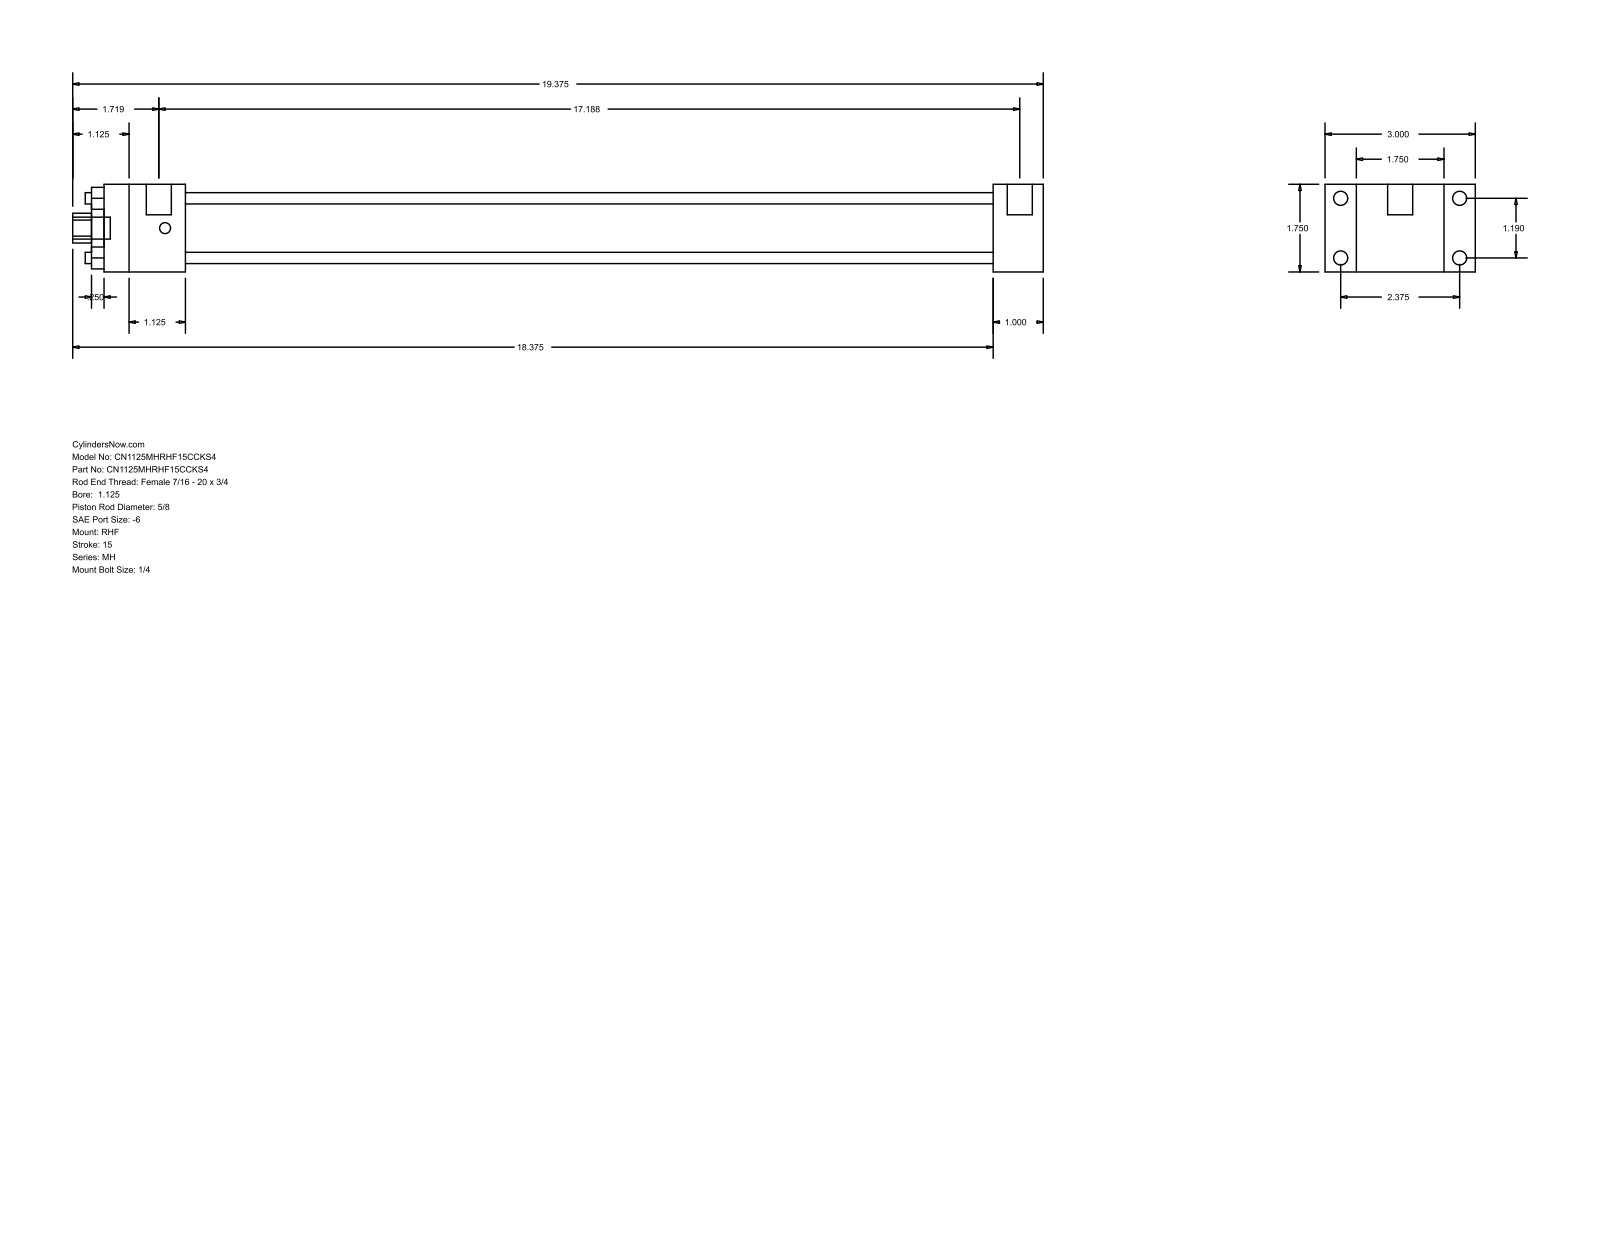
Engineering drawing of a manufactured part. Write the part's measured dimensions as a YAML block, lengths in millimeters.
part_name: "MH_RHF__0112_0.625"
step_written_by: "GSSL Pune (CONFIG_CONTROL_DESIGN)"
units: millimeters
bodies: {solids: 0, faces: 88, planar: 60, cylindrical: 28, other: 0}
overall_size: [492.12, 76.2, 44.45]
round_holes:
  - {diameter: 5.71, count: 4}
  - {diameter: 15.88, count: 1}
  - {diameter: 28.57, count: 1}
  - {diameter: 34.92, count: 1}
round_bosses_or_shafts:
  - {diameter: 7.14, count: 4}
  - {diameter: 5.56, count: 4}
  - {diameter: 12.7, count: 2}
  - {diameter: 11.11, count: 1}
partial_cylinders:
  - {radius: 7.54, count: 1}
face_to_face_distances: [44.46, 15.87, 60.33, 25.39, 76.2, 409.58, 434.97, 41.27, 450.85, 476.24]
hole_center_spacings: [21.37, 30.22, 42.74]
